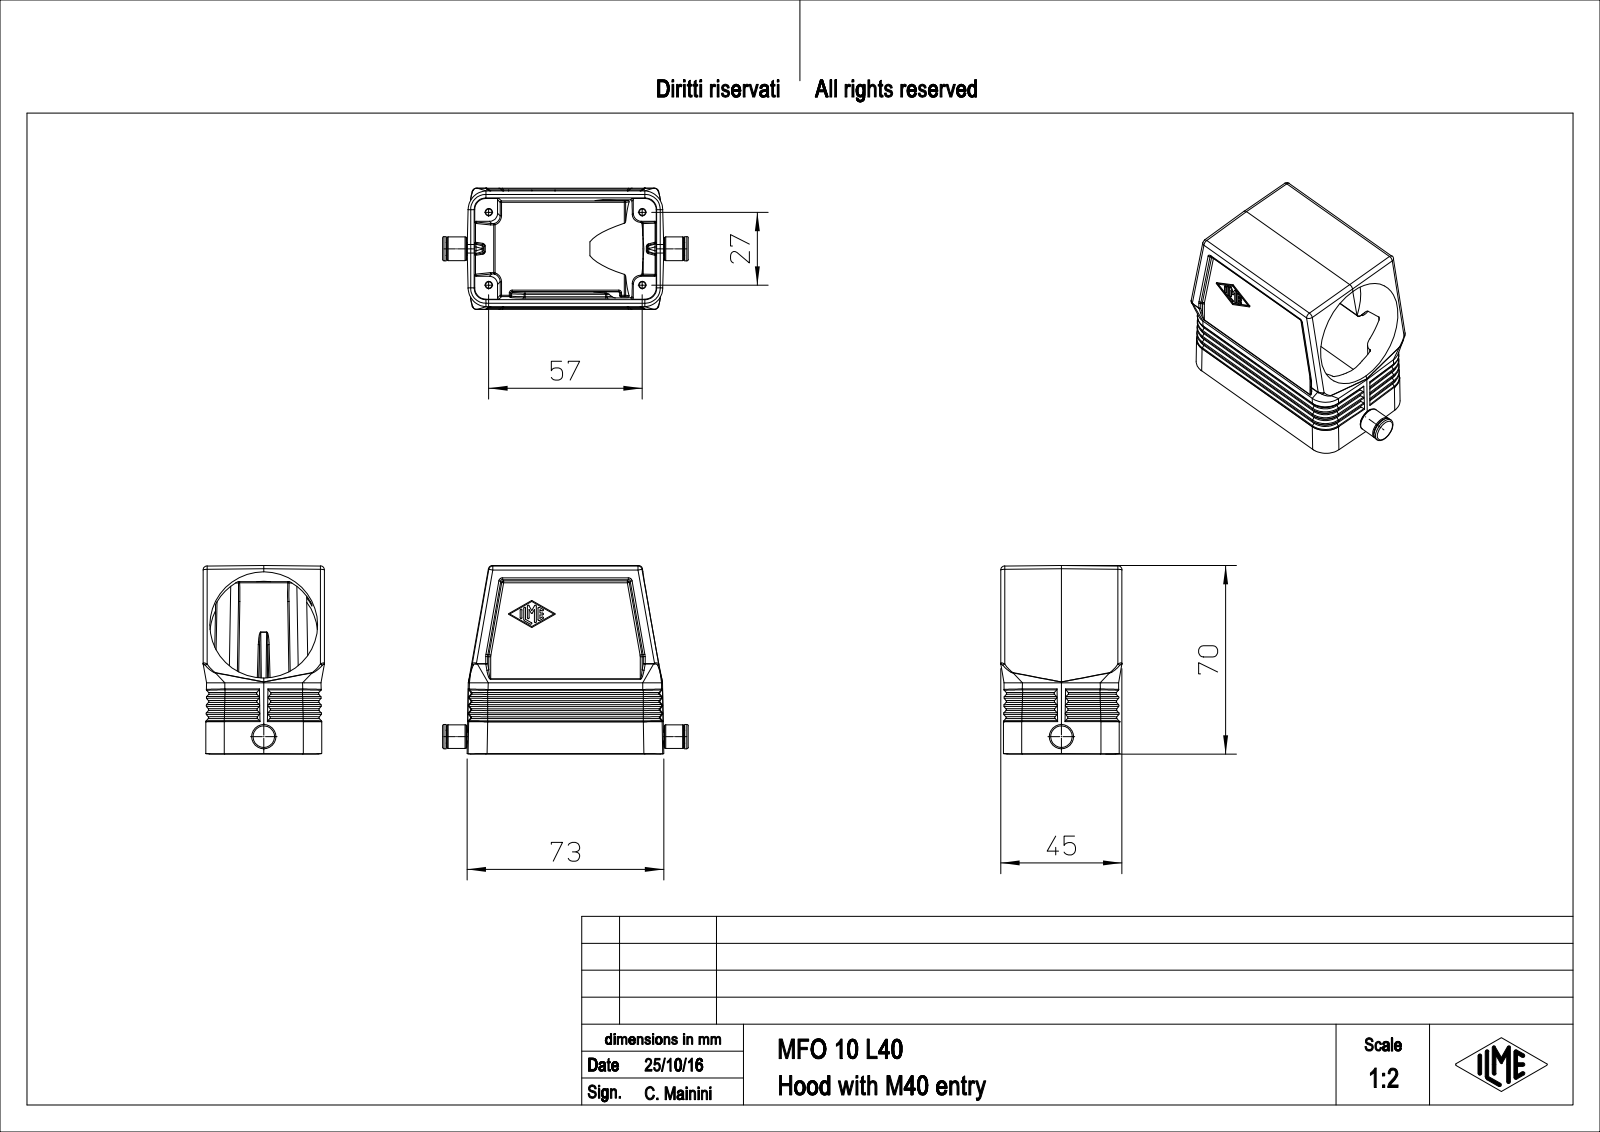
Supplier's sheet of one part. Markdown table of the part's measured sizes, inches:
| quantity | value |
| --- | --- |
| part name | MFO_10_L40 |
| STEP written by | PTC Creo Elements/Direct Modeling 19.0E 27-Jun-2016 (C) Parametric Technology GmbH (AUTOMOTIVE_DESIGN) |
| units | inches |
| bodies | 1 solid, 410 faces (155 planar, 88 cylindrical, 167 other) |
| overall size | 3.59 × 2.756 × 1.772 |
| volume | 3.733 in³ |
| surface area | 50.95 in² |
| round holes (diameter × count) | 0.108 × 4, 1.575 × 1 |
| round bosses / shafts (diameter × count) | 0.354 × 1, 0.346 × 1, 0.189 × 1, 0.126 × 1 |
| partial cylindrical surfaces (radius × count) | 0.02 × 17, 0.059 × 10, 0.276 × 8, 0.118 × 4, 0.165 × 4, 0.236 × 4, 0.787 × 1 |
| main face-to-face distances | 1.693, 0.335, 0.079, 0.075, 1.732, 0.039, 0.157, 1.772, 0.236, 0.447 |
| hole center spacings | 1.063, 2.244, 2.483 |
